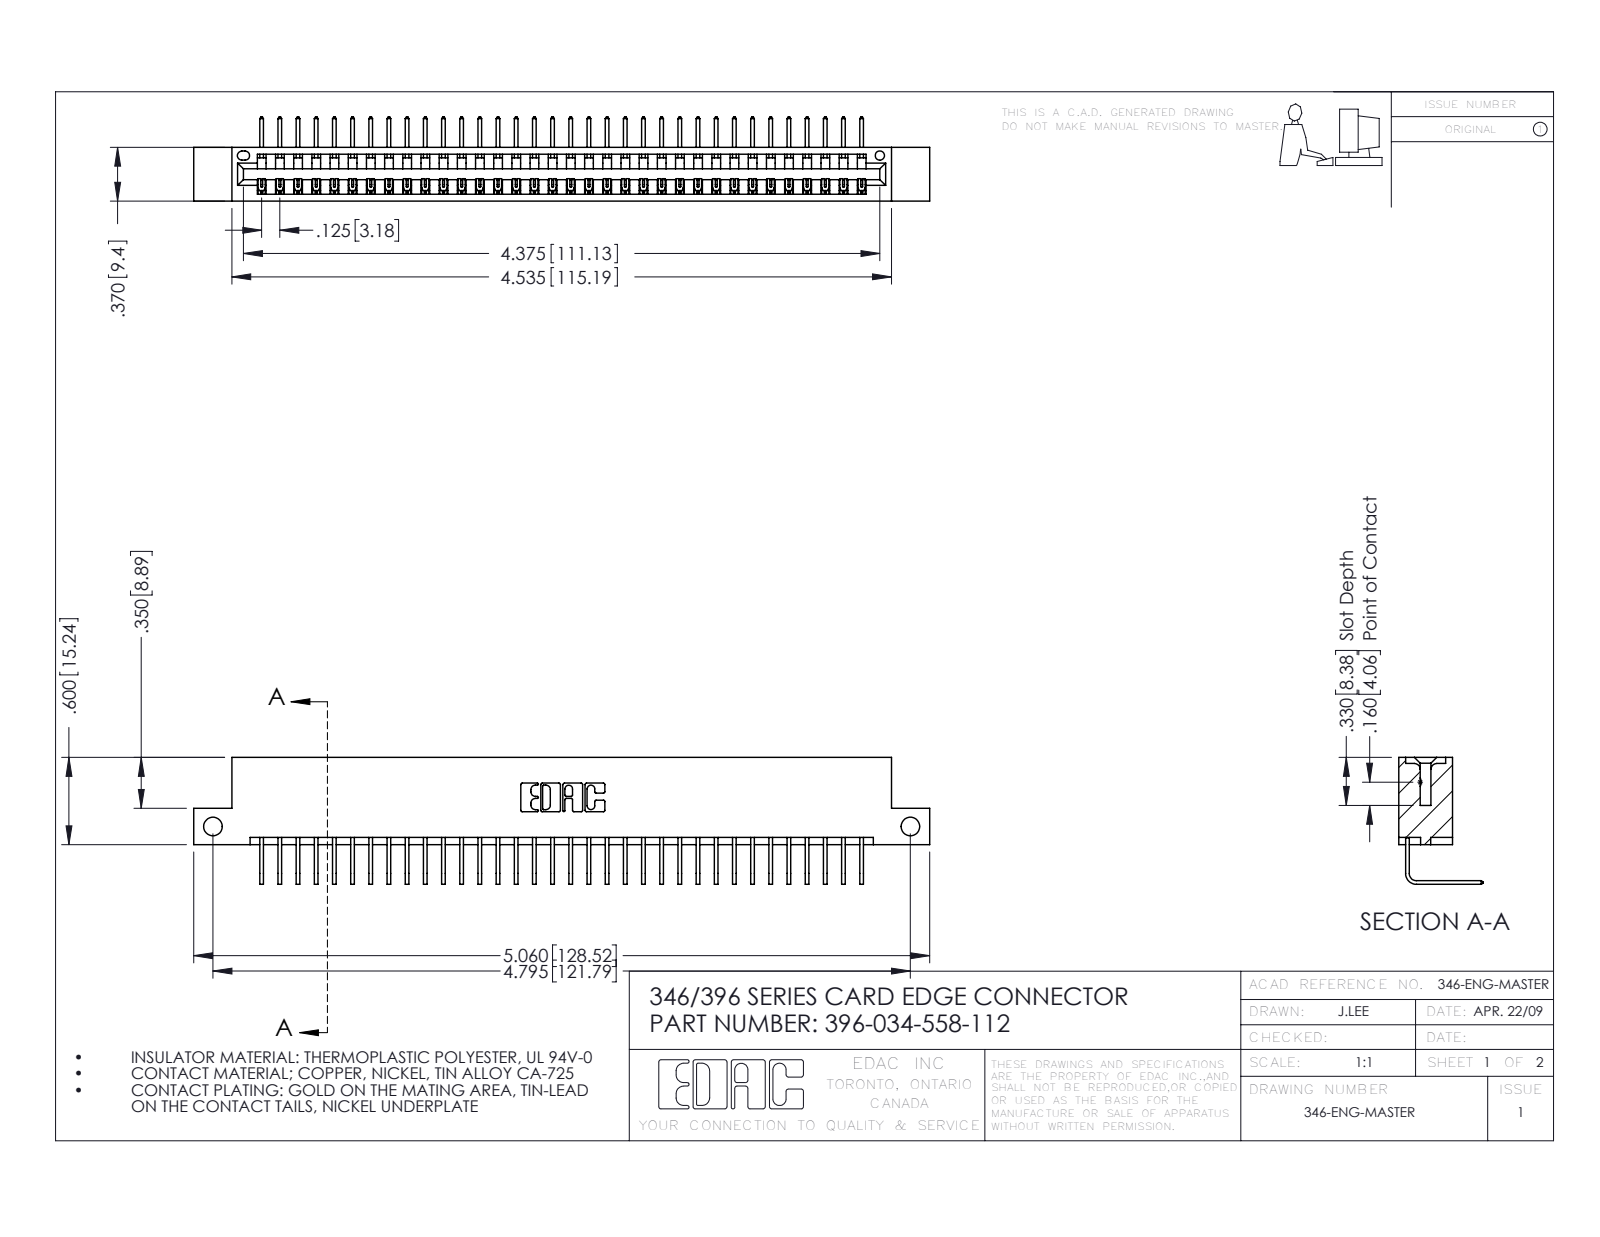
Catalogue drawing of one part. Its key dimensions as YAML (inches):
part_name: "345-292-001_558 Tail - 2; 346 Part_Flush Mounting Lugs - Side Mount; 396-034-558-112"
step_written_by: "SolidWorks 2016 (CONFIG_CONTROL_DESIGN)"
units: inches
bodies: {solids: 35, faces: 2162, planar: 1504, cylindrical: 658, other: 0}
overall_size: [5.06, 0.873, 0.58]
volume: 0.749
surface_area: 24.47
round_holes:
  - {diameter: 0.128, count: 2}
  - {diameter: 0.064, count: 1}
partial_cylinders:
  - {radius: 0.006, count: 68}
  - {radius: 0.01, count: 22}
  - {radius: 0.007, count: 6}
  - {radius: 0.031, count: 6}
  - {radius: 0.026, count: 3}
  - {radius: 0.031, count: 2}
  - {radius: 0.04, count: 2}
  - {radius: 0.014, count: 1}
face_to_face_distances: [0.322, 0.048, 0.37, 0.25, 0.298, 0.025, 0.072, 0.148, 0.222, 0.1]
hole_center_spacings: [4.795]
